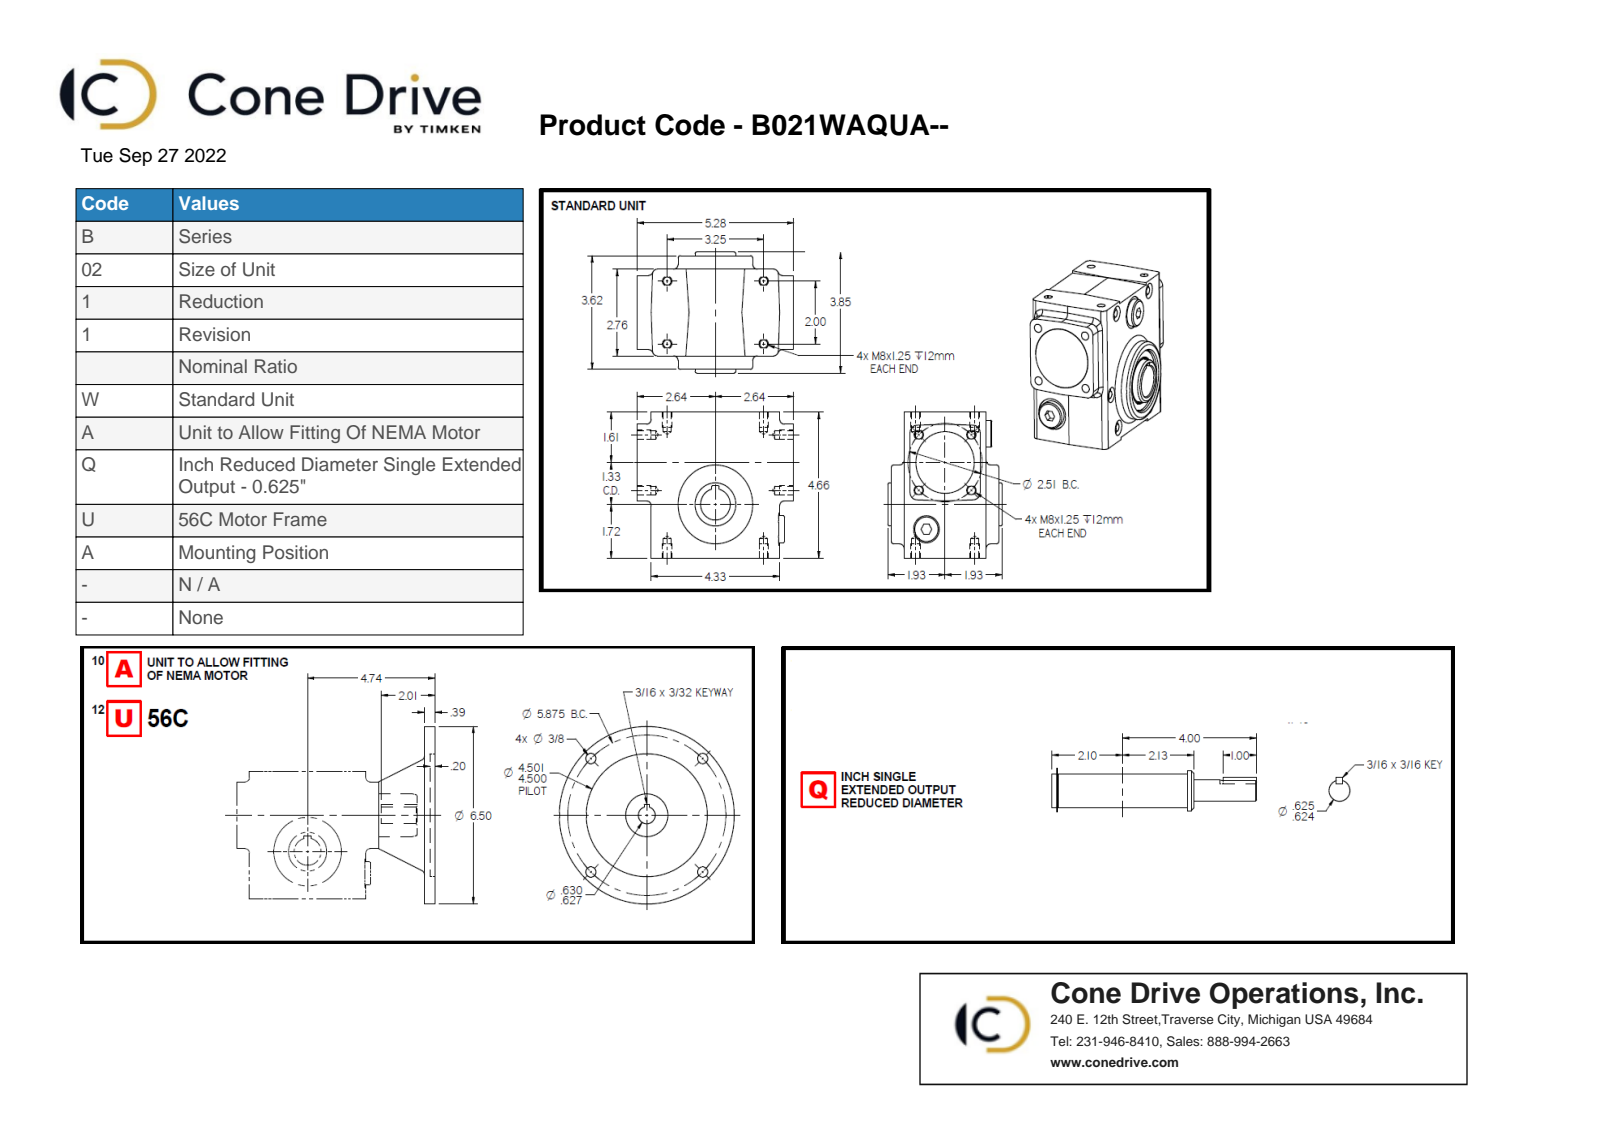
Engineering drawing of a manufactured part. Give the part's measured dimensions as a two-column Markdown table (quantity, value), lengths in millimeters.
| quantity | value |
| --- | --- |
| part name | B021115.WAQUA; B02-1-CP; B02-0Q-CP; B02U-CP |
| STEP written by | Solid Edge (AUTOMOTIVE_DESIGN) |
| units | millimeters |
| bodies | 13 solids, 537 faces (286 planar, 139 cylindrical, 112 other) |
| overall size | 187.41 × 184.15 × 165.1 |
| volume | 1 185 000 mm³ |
| surface area | 219 933 mm² |
| round holes (diameter × count) | 12.5 × 6, 6.65 × 4, 6.92 × 4, 8.8 × 4, 9.6 × 4, 1.98 × 2, 26 × 2, 12.7 × 1, 15.94 × 1, 25.4 × 1, 28.19 × 1, 28.4 × 1 |
| round bosses / shafts (diameter × count) | 10 × 6, 6 × 6, 12.85 × 4, 0.51 × 3, 22 × 2, 165.1 × 1, 63.84 × 1, 50 × 1 |
| partial cylindrical surfaces (radius × count) | 4 × 12, 3.98 × 4, 6 × 4, 7.5 × 4, 0.2 × 2, 0.61 × 2, 2.54 × 2, 12.7 × 2 |
| main face-to-face distances | 10, 70.08, 5, 43.39, 53.39, 118.37, 134.03, 118.25, 48.39, 4 |
| hole center spacings | 81.12, 31.82, 42.79, 45, 74.61, 105.52, 106.43, 14.51 |
